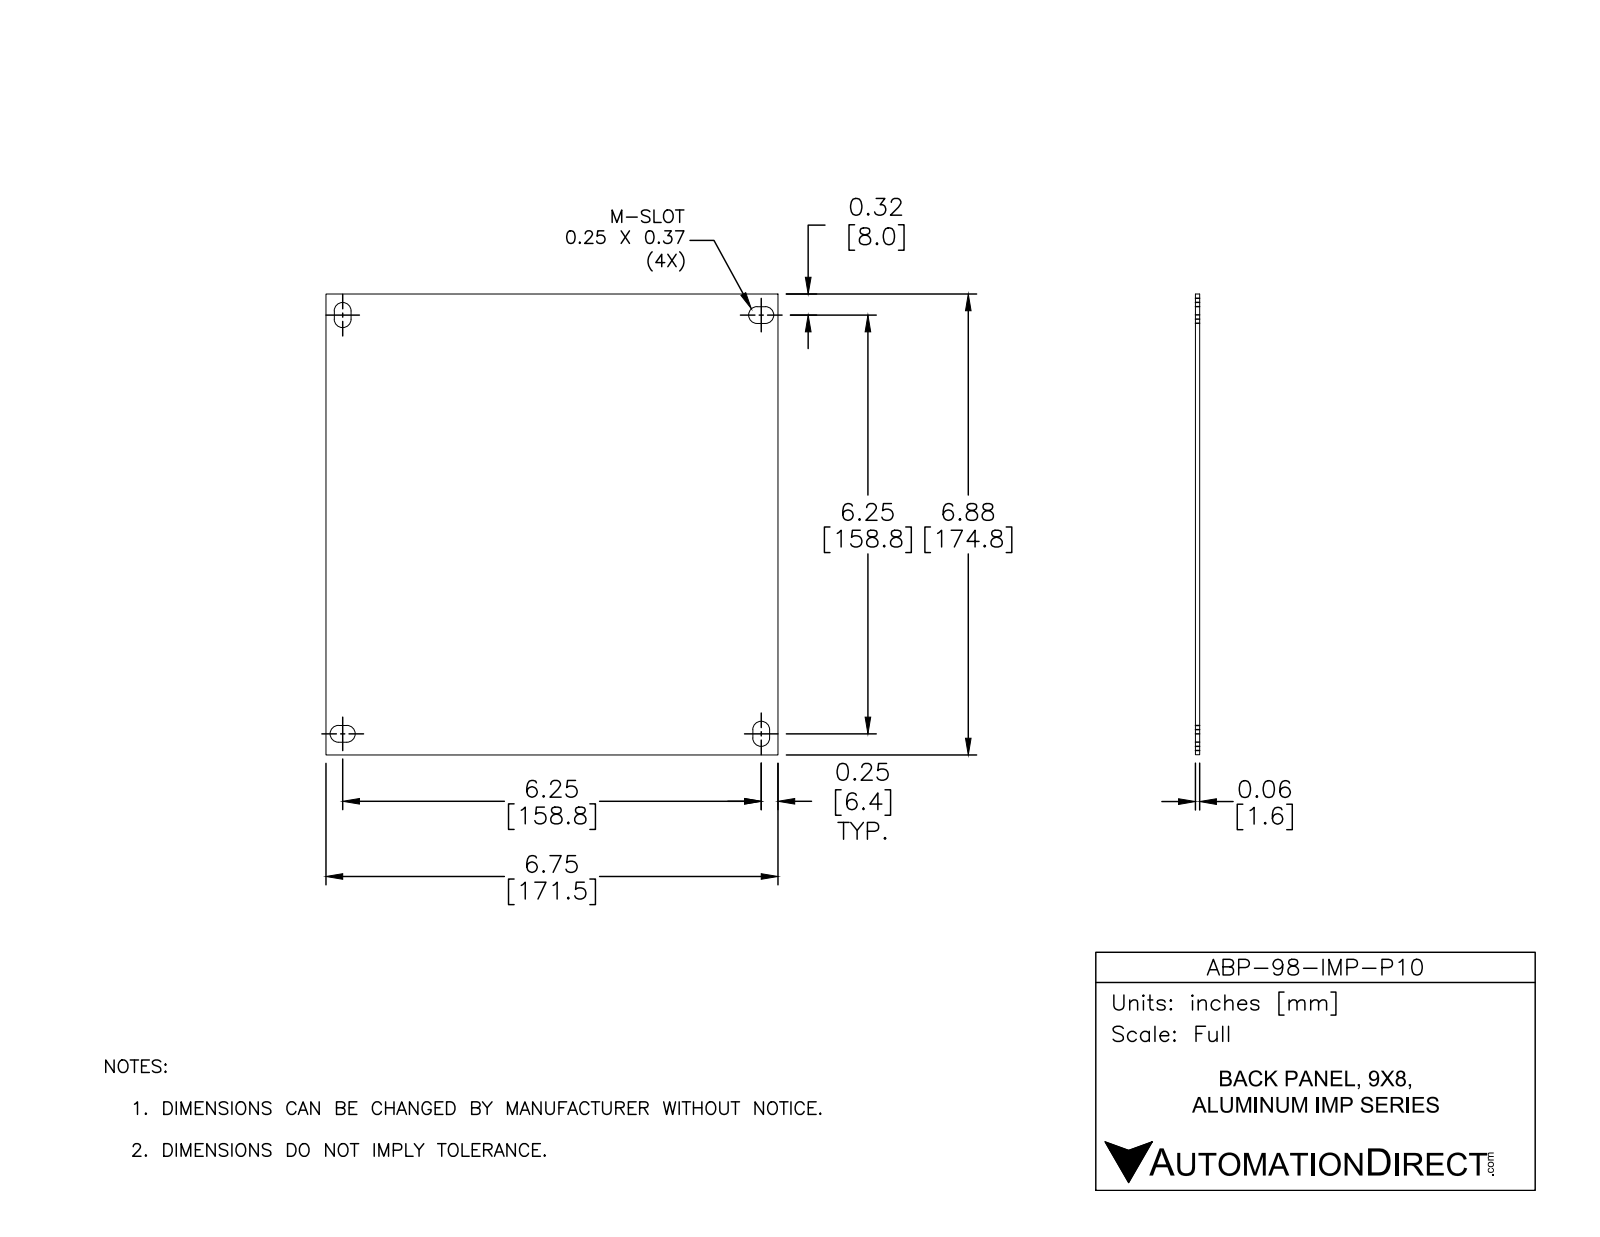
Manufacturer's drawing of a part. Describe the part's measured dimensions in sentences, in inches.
The part is named "ABP-98-IMP-P604". Its 3-D file was written by "SolidWorks 2016 (AUTOMOTIVE_DESIGN)". It is 1 solid with 24 faces: 14 planar, 10 cylindrical and 0 other. Overall it measures 6.88 by 6.75 by 0.064 inches. Its volume is 2.956 cubic inches and its surface area 94.25 square inches. Partial cylindrical surfaces (rounded edges, fillets, slot ends): 8 of radius 0.125. The main face-to-face distances are 0.064, 6.75, 6.88, 0.25, 6.25, 0.125, 6.625, 6, 6.375, 0.25.
